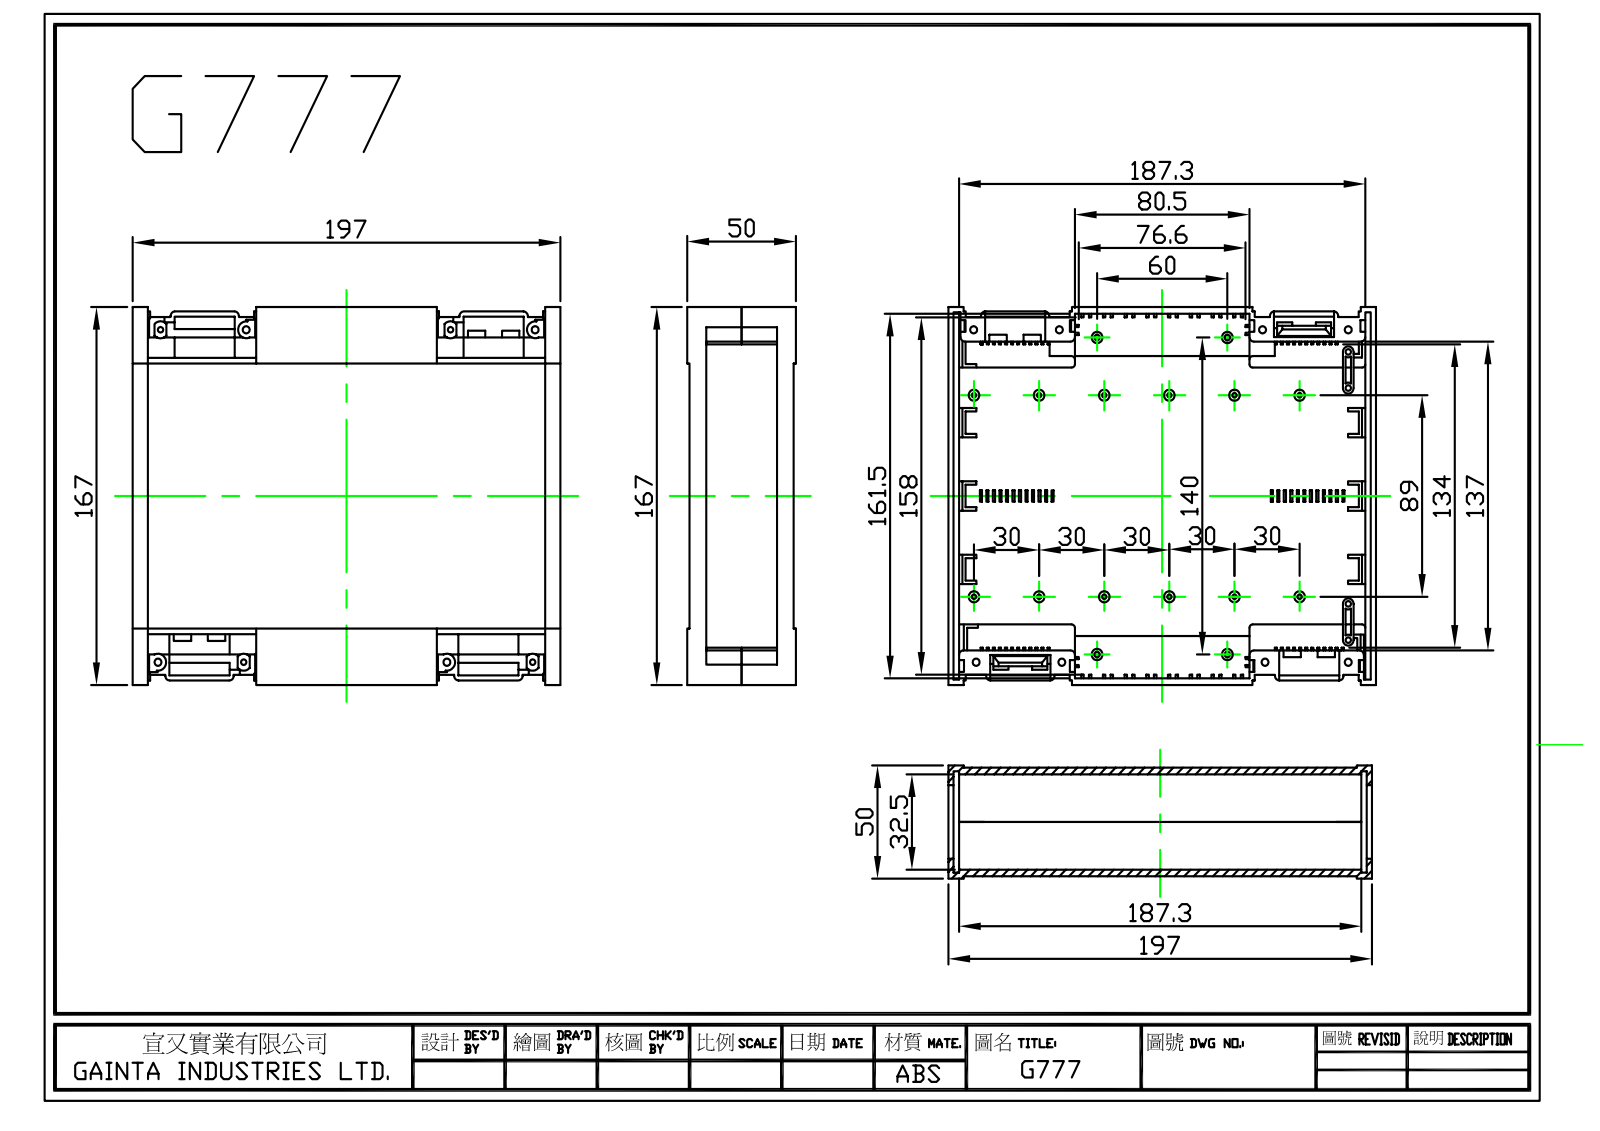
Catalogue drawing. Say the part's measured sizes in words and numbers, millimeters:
The part is named "G777". Its 3-D file was written by "SolidWorks 2012 (AUTOMOTIVE_DESIGN)". It is 10 solids with 4308 faces: 2784 planar, 1114 cylindrical and 410 other. Overall it measures 197 by 168 by 50 millimeters. Its volume is 293 319 cubic millimeters and its surface area 272 637 square millimeters. Round holes: 20 of diameter 2.2, 8 of diameter 2.7, 8 of diameter 3.5. Round bosses or shafts: 4 of diameter 5. Partial cylindrical surfaces (rounded edges, fillets, slot ends): 96 of radius 0.2, 48 of radius 1, 20 of radius 1.5, 16 of radius 0.1, 12 of radius 0.5, 8 of radius 3, 8 of radius 4, 8 of radius 7. The main face-to-face distances are 2.5, 42.5, 45, 2, 40, 5, 47.5, 3, 0.5, 166. The hole center spacings are 90, 30, 60, 94.87, 108.17, 17.52, 25, 36.26.
